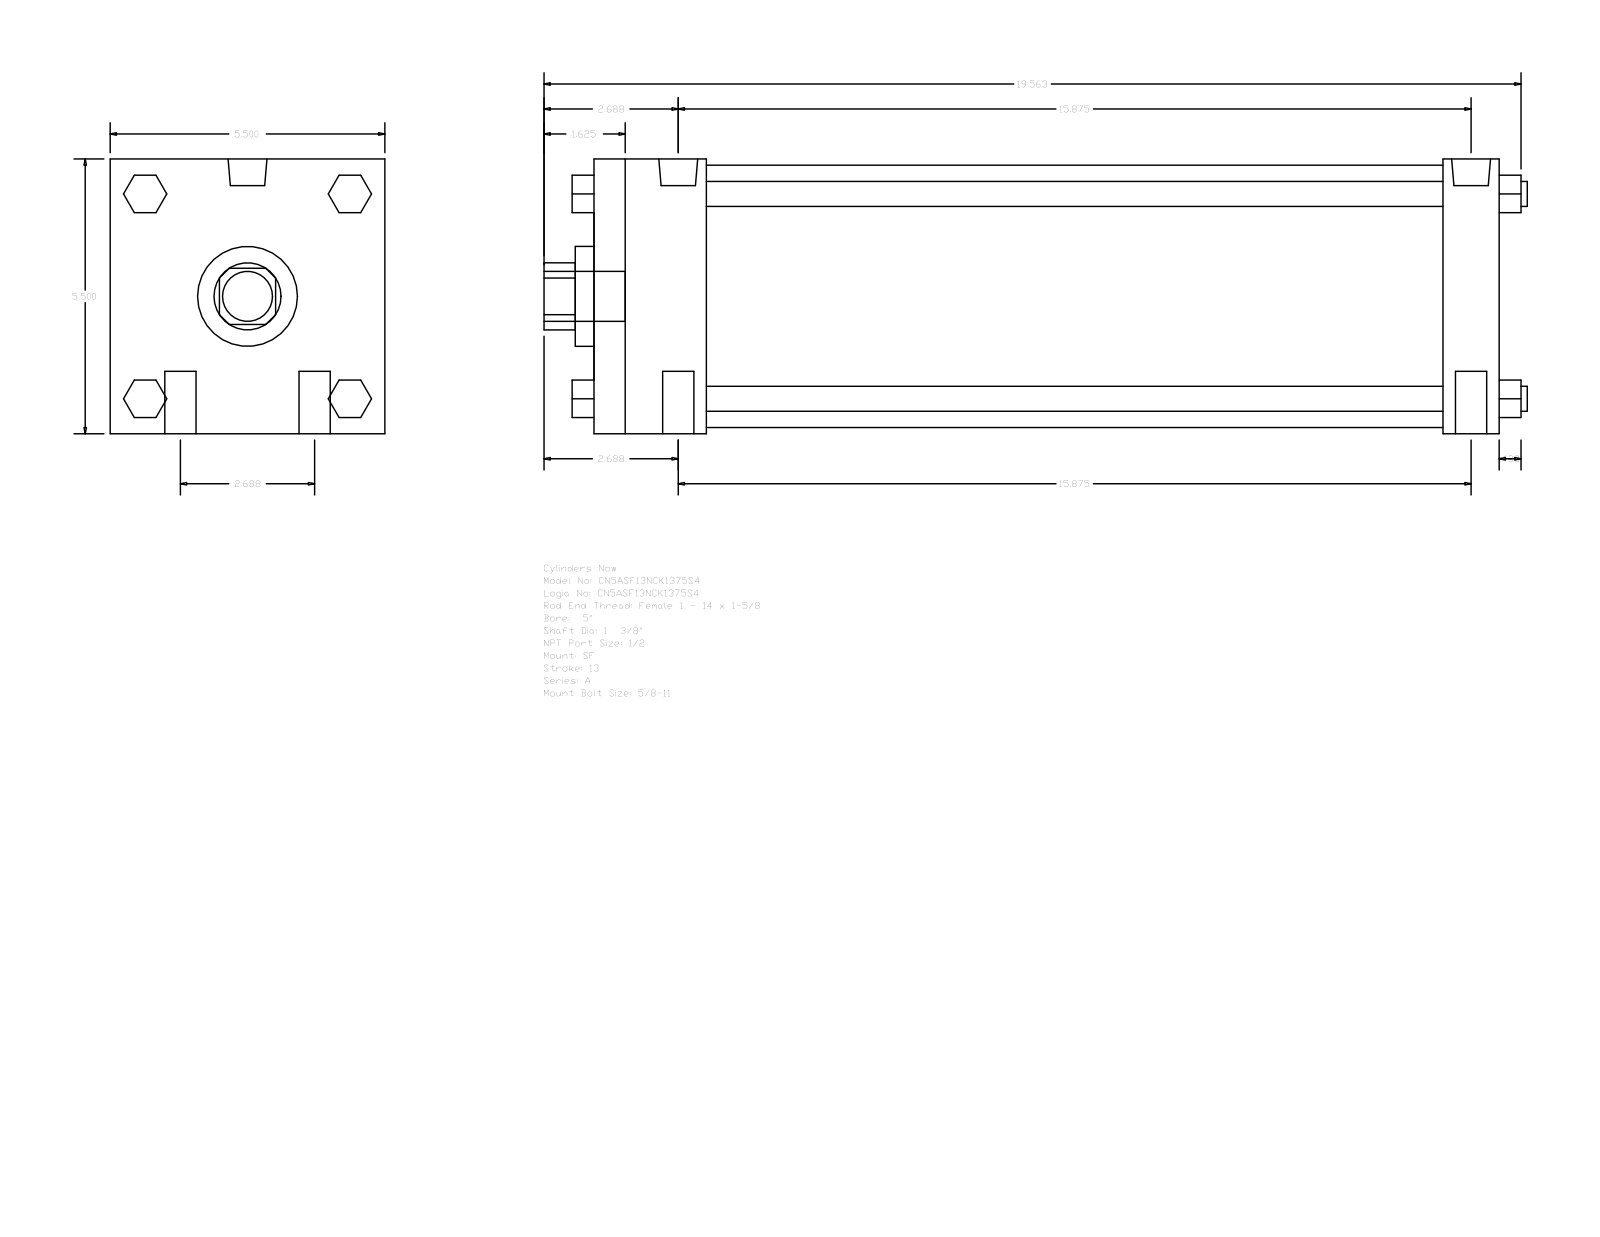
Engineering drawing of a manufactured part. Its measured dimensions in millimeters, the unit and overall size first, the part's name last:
Units: millimetres
Overall size (bounding box): 500.06 × 139.7 × 139.7
Round holes (diameter × count): ⌀34.92 ×1, ⌀50.8 ×1, ⌀133.35 ×1
Round bosses / shafts (diameter × count): ⌀15.88 ×4, ⌀12.7 ×4, ⌀19.77 ×2, ⌀8.73 ×2, ⌀25.4 ×1
Partial cylindrical surfaces — rounded edges, fillets, slot ends (radius × count): R17.06 ×1
Main face-to-face distances: 139.7, 460.37, 28.57, 57.15, 431.8, 374.65, 403.22, 19.05, 52.07, 90.18
Bodies: 0 solids, 124 faces (94 planar, 30 cylindrical, 0 other)
Part name (STEP PRODUCT): A_SF__0500_1.375
STEP written by: GSSL Pune (CONFIG_CONTROL_DESIGN)
